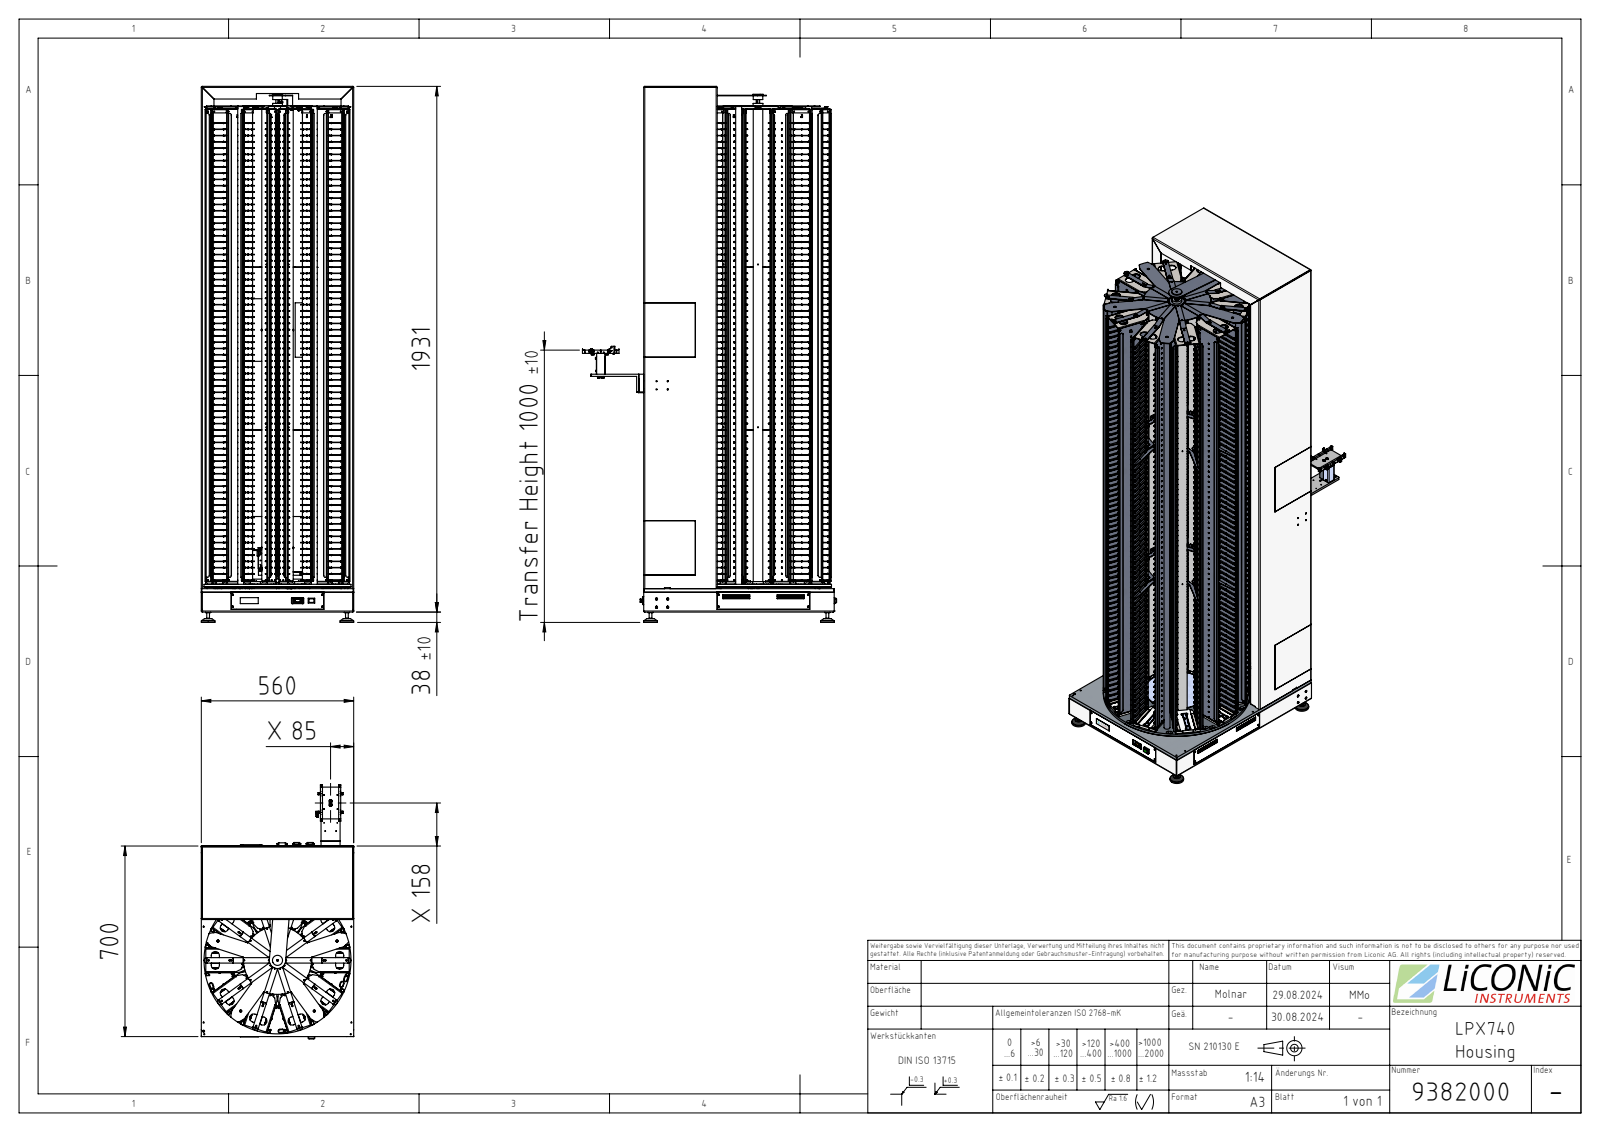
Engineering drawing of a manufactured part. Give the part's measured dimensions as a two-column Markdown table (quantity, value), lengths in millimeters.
| quantity | value |
| --- | --- |
| part name | 9382000 |
| STEP written by | SolidWorks 2022 (AUTOMOTIVE_DESIGN) |
| units | millimeters |
| bodies | 69 solids, 9466 faces (4895 planar, 4434 cylindrical, 137 other) |
| overall size | 1969 × 933.98 × 560.01 |
| volume | 18 470 000 mm³ |
| surface area | 9 971 000 mm² |
| round holes (diameter × count) | 4 × 178, 2.5 × 79, 4.2 × 71, 3.3 × 57, 4.4 × 30, 6.5 × 28, 3 × 20, 7.1 × 16, 8 × 13, 3.4 × 10, 6.2 × 10, 3.1 × 8 |
| round bosses / shafts (diameter × count) | 22 × 5, 50.01 × 4, 10 × 4, 1.5 × 3, 540 × 1, 234 × 1, 15.5 × 1, 14.5 × 1 |
| partial cylindrical surfaces (radius × count) | 0.1 × 832, 0.25 × 832, 2 × 697, 1 × 136, 5 × 121, 2.5 × 114, 3 × 66, 1.7 × 40 |
| main face-to-face distances | 2, 558, 72, 560, 556, 1, 74, 1857, 268, 12 |
| hole center spacings | 23, 46, 69, 92, 115, 138, 161, 184 |
